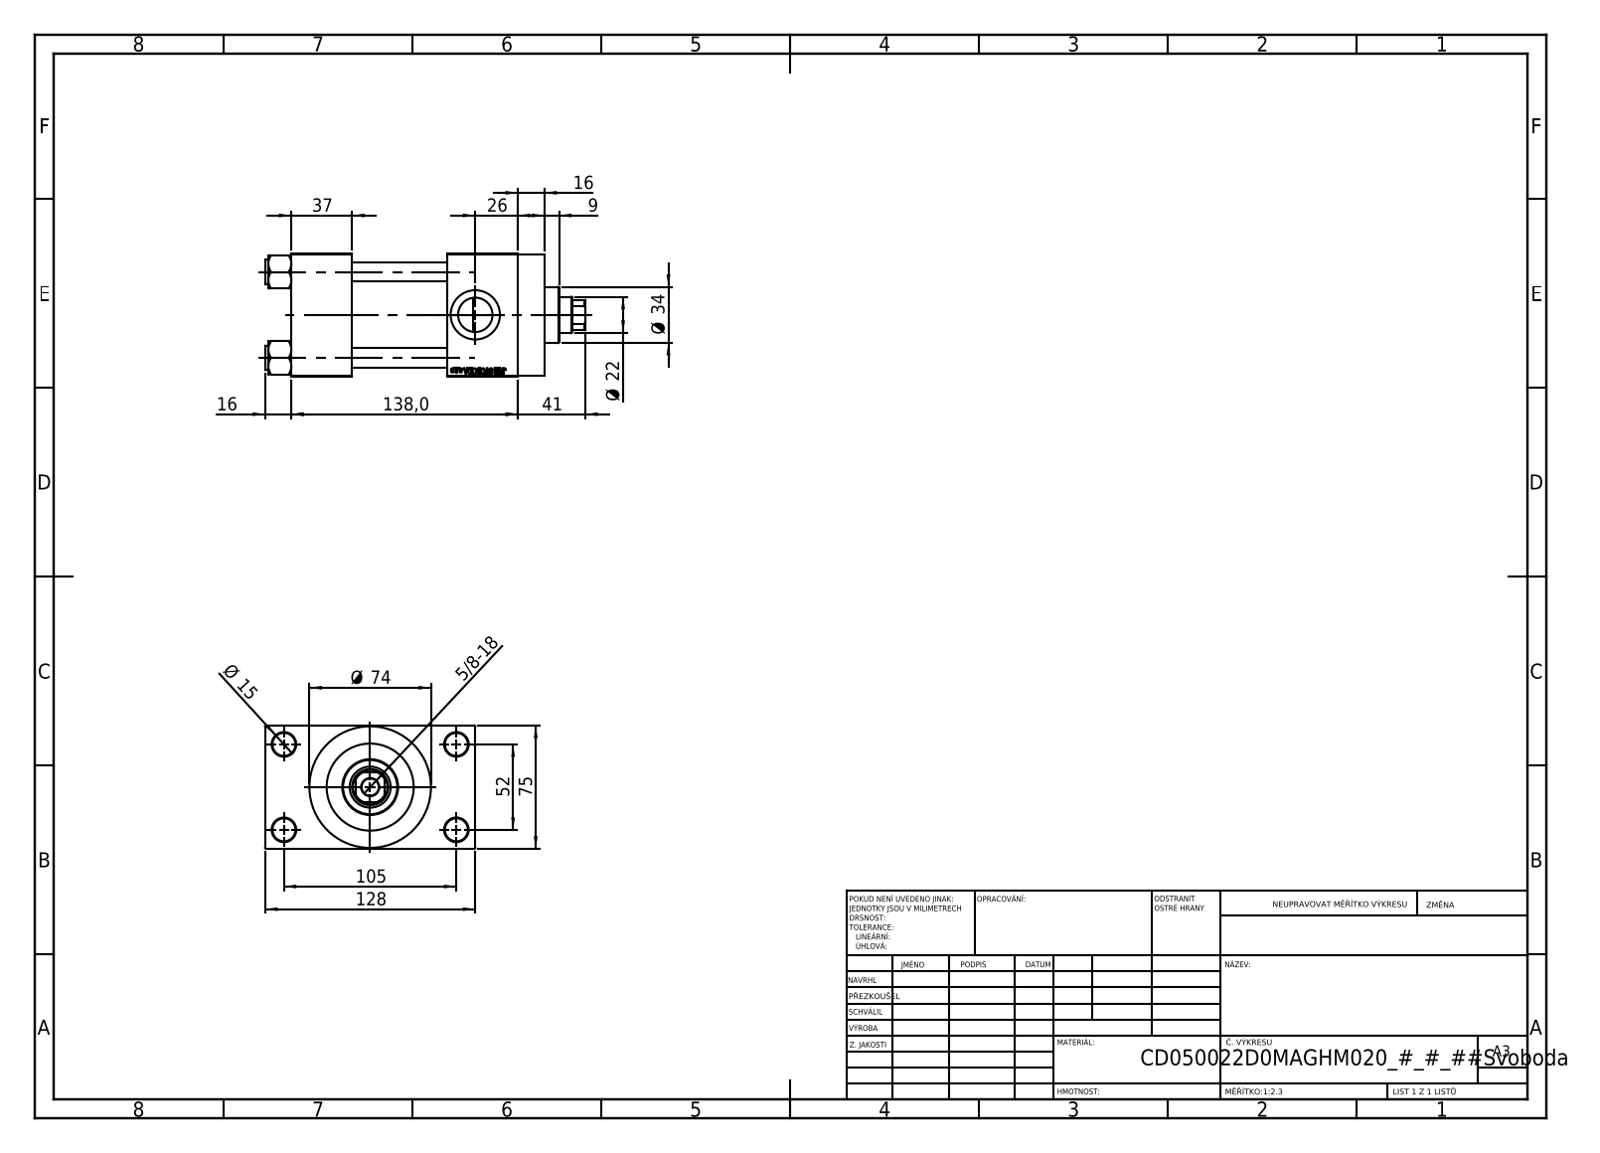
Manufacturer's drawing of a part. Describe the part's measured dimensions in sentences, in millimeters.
The part is named "V215CD_D_Body; V215CD_VCP_D; V215CD_NUT_M5_D; V215CD_VC_A (+1 more)". Its 3-D file was written by "SolidWorks 2019 (CONFIG_CONTROL_DESIGN)". It is 11 solids with 1104 faces: 497 planar, 89 cylindrical and 518 other. Overall it measures 195 by 128 by 75 millimeters. Its volume is 797 396 cubic millimeters and its surface area 166 692 square millimeters. Round holes: 4 of diameter 12, 4 of diameter 14, 2 of diameter 7, 2 of diameter 20.96, 2 of diameter 30, 1 of diameter 10.5, 1 of diameter 22, 1 of diameter 25, 1 of diameter 41, 1 of diameter 50, 1 of diameter 53. Round bosses or shafts: 4 of diameter 15, 1 of diameter 74, 1 of diameter 56, 1 of diameter 34. Partial cylindrical surfaces (rounded edges, fillets, slot ends): 1 of radius 10.5. The main face-to-face distances are 75, 58, 37, 95, 26.5, 101.5, 138, 101, 43, 16. The hole center spacings are 26.35, 36.98, 52.3, 58.43, 58.59, 78.65, 94.37, 52.
